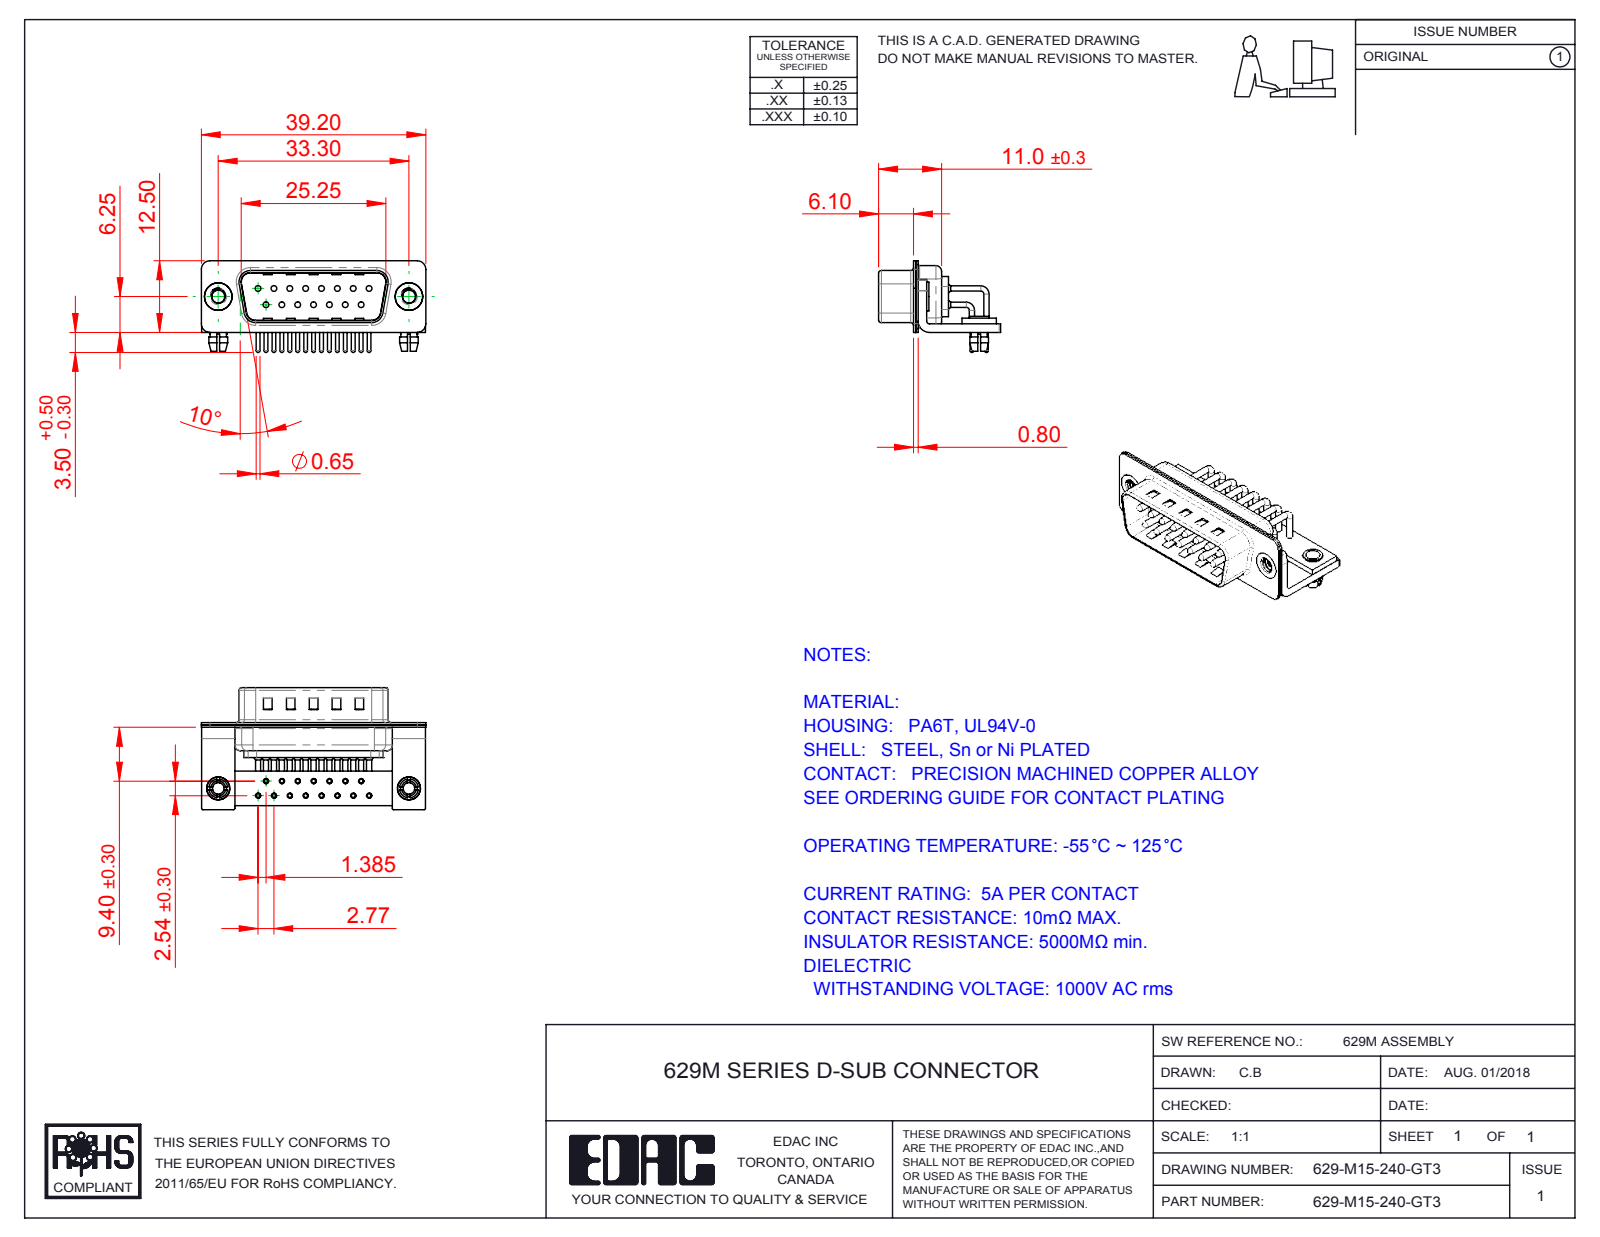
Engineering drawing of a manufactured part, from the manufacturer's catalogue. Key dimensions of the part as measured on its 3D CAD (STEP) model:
Part name (STEP PRODUCT): 629M Housing_15 Contacts; 629M Contact Row 2; 629M Stabilizer Bracket; 629M Contact Row 1 (+6 more)
STEP written by: SolidWorks 2016 (CONFIG_CONTROL_DESIGN)
Units: millimetres
Bodies: 25 solids, 2162 faces (1173 planar, 757 cylindrical, 232 other)
Overall size (bounding box): 39.2 × 21.3 × 16
Volume: 2 481 mm³ · Surface area: 6 762 mm²
Round holes (diameter × count): ⌀2 ×17, ⌀0.9 ×15, ⌀1 ×15, ⌀1.7 ×15, ⌀2.26 ×2, ⌀2.5 ×2, ⌀3.2 ×2, ⌀4 ×2, ⌀4.8 ×2
Round bosses / shafts (diameter × count): ⌀0.9 ×21, ⌀1.5 ×15, ⌀0.65 ×15, ⌀5 ×2, ⌀4.9 ×2, ⌀4 ×2, ⌀3.4 ×2, ⌀3.3 ×2
Partial cylindrical surfaces — rounded edges, fillets, slot ends (radius × count): R0.25 ×16, R1.5 ×16, R1.01 ×15, R2 ×13, R0.5 ×9, R1.6 ×8, R0.6 ×4, R0.65 ×4
Main face-to-face distances: 0.4, 1.5, 0.85, 0.8, 1.25, 10.4, 9.55, 1, 1.9, 9.15
Hole centre spacings: 2.77, 5.54, 3.16, 8.31, 4.87, 11.08, 2.89, 7.37
